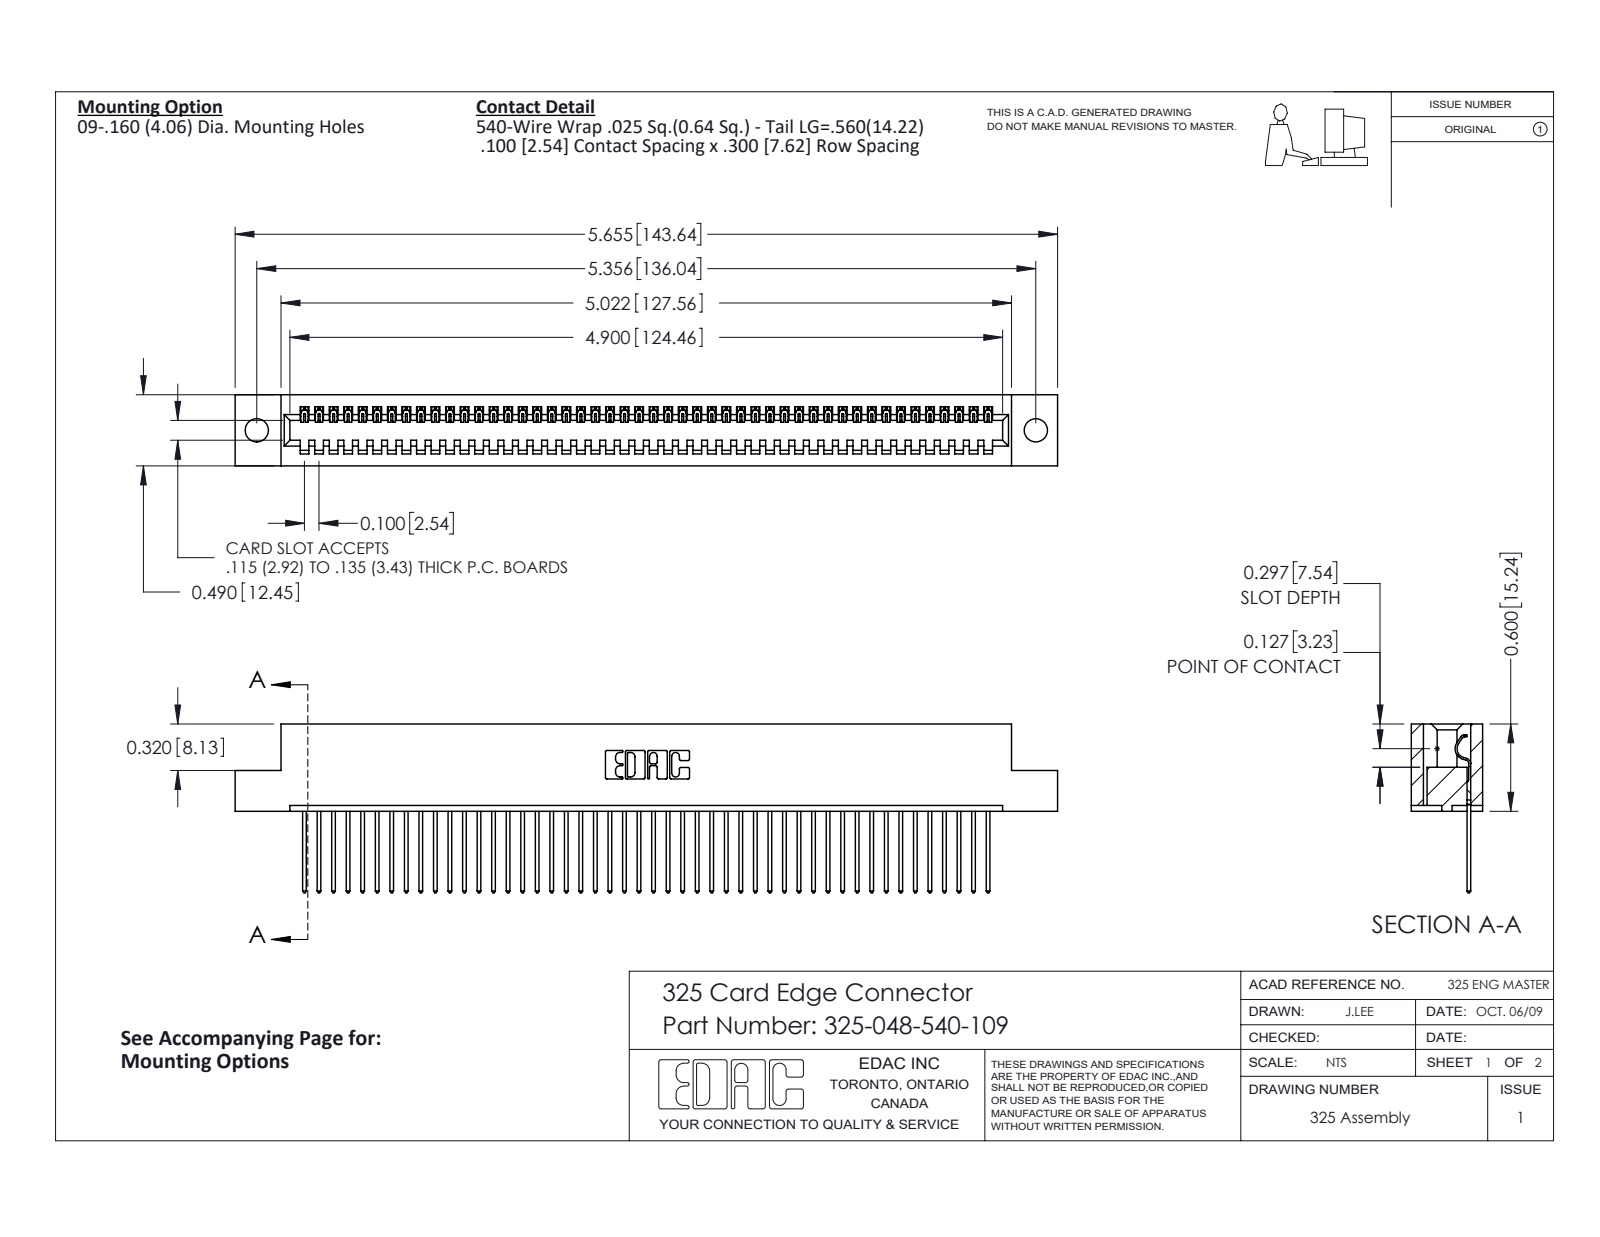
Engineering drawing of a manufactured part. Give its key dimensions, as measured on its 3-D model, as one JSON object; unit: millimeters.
{"part_name": "325 Part_.160 TH; 325-292-001_325-293-140; 325-048-540-109", "step_written_by": "SolidWorks 2016 (CONFIG_CONTROL_DESIGN)", "units": "millimeters", "bodies": {"solids": 49, "faces": 2898, "planar": 2086, "cylindrical": 812, "other": 0}, "overall_size": [143.6, 29.5, 12.4], "volume_mm3": 18120, "surface_area_mm2": 20270, "round_holes": [[4.1, 2]], "partial_cylinders_radius": [[0.2, 96], [0.3, 96], [0.3, 22], [0.2, 6], [0.8, 6], [0.7, 3], [0.4, 1], [0.6, 1]], "face_to_face_distances": [2.1, 10.3, 12.4, 7.6, 2.7, 9.7, 0.6, 8.3, 14.2, 6.7], "hole_center_spacings": [136]}
